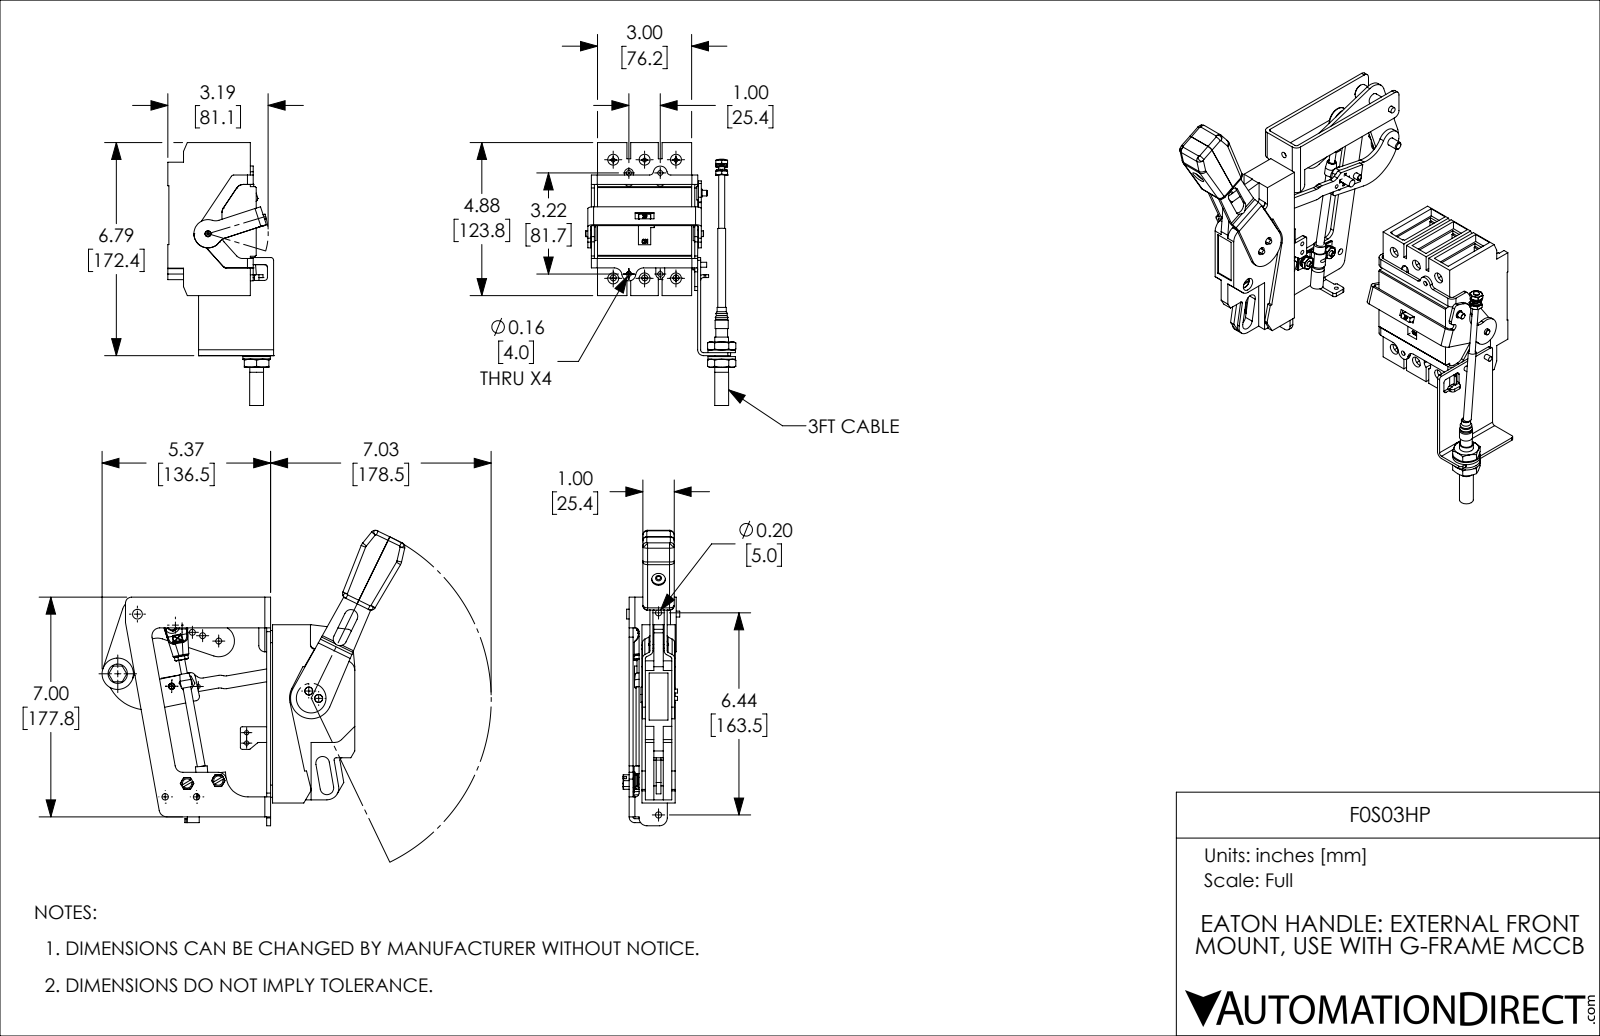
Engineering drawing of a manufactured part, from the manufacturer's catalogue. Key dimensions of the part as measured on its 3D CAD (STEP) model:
Part name (STEP PRODUCT): F0S03HP_HANDLE; F0S03HP; F0S03HP_BREAKER
STEP written by: SolidWorks 2019 (CONFIG_CONTROL_DESIGN)
Units: inches
Bodies: 77 solids, 2152 faces (1122 planar, 779 cylindrical, 251 other)
Overall size (bounding box): 11.71 × 10.066 × 9.651
Volume: 51.14 in³ · Surface area: 437.6 in²
Round holes (diameter × count): ⌀0.156 ×8, ⌀0.188 ×8, ⌀0.203 ×6, ⌀0.348 ×6, ⌀0.19 ×5, ⌀0.125 ×3, ⌀0.125 ×3, ⌀0.194 ×3, ⌀0.196 ×3, ⌀0.25 ×3, ⌀0.253 ×3, ⌀0.136 ×2
Round bosses / shafts (diameter × count): ⌀0.25 ×9, ⌀0.375 ×5, ⌀0.44 ×4, ⌀0.375 ×3, ⌀0.344 ×3, ⌀0.312 ×3, ⌀0.243 ×3, ⌀0.181 ×3
Partial cylindrical surfaces — rounded edges, fillets, slot ends (radius × count): R0.25 ×31, R0.09 ×23, R0.062 ×17, R0.125 ×17, R0.02 ×12, R0.15 ×12, R0.032 ×11, R0.031 ×10
Main face-to-face distances: 0.094, 0.125, 0.594, 5.342, 8.342, 3, 5.467, 8.467, 0.187, 0.11
Hole centre spacings: 1, 2, 0.017, 0.647, 3.396, 3.663, 3.9, 5.57
